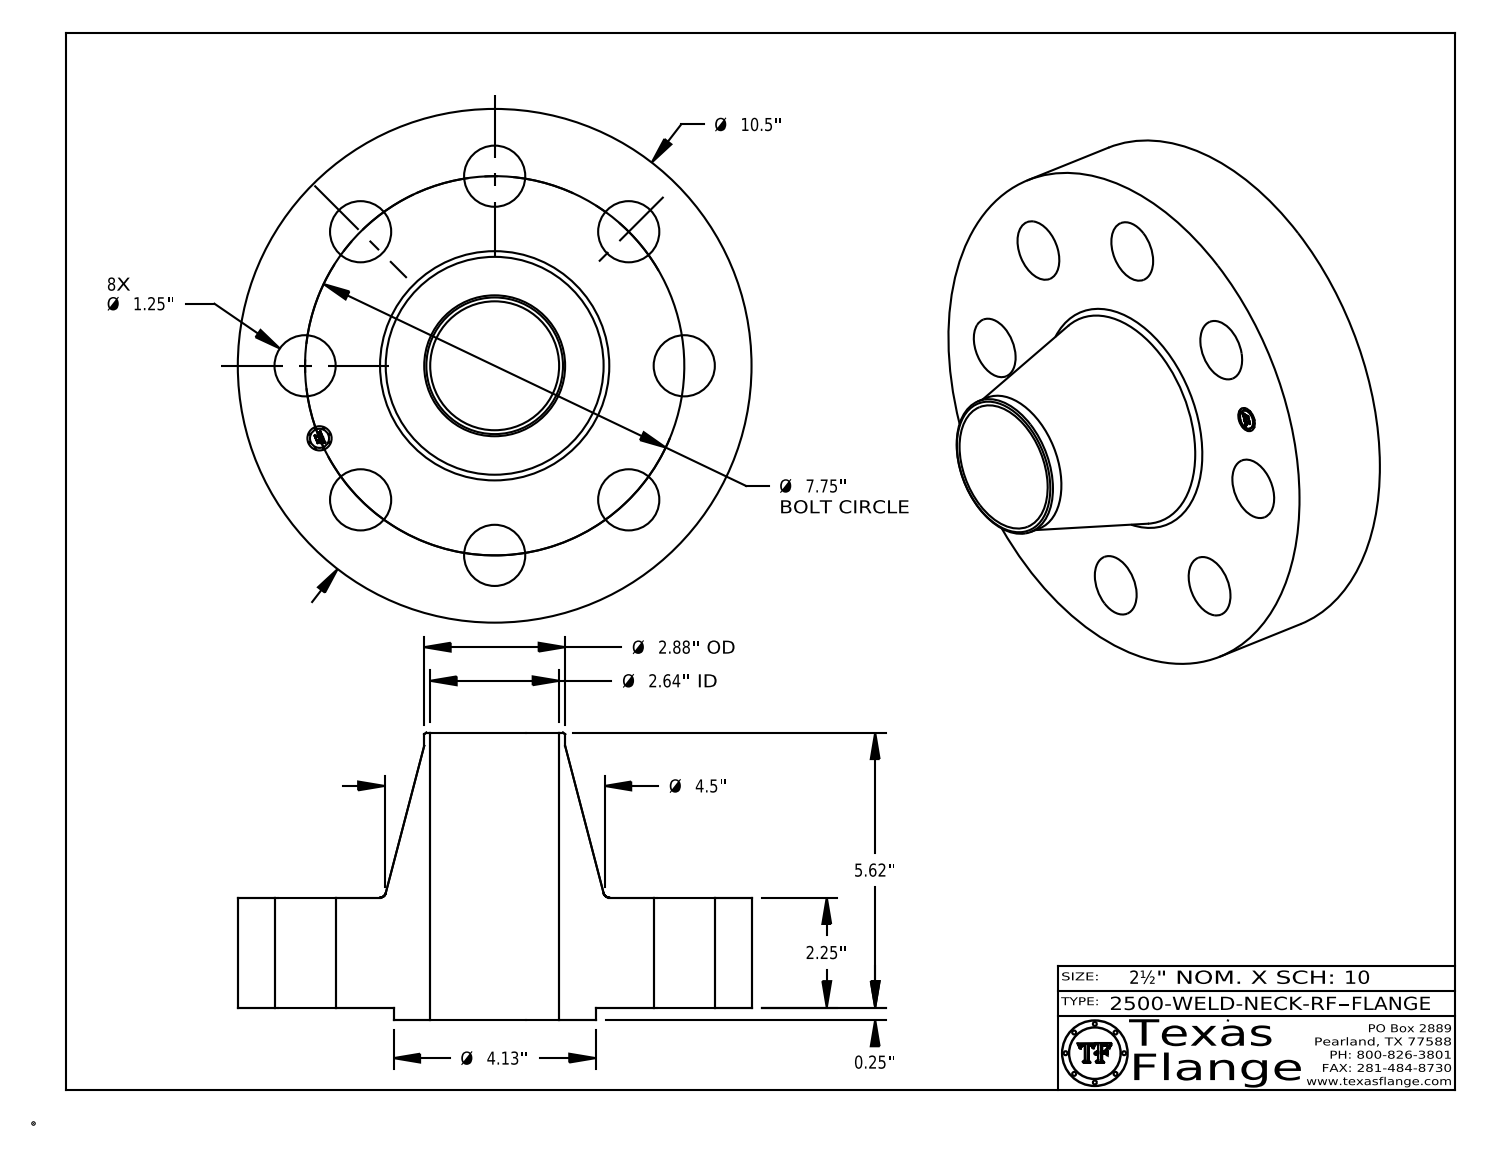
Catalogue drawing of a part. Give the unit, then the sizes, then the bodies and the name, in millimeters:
Units: millimetres
Overall size (bounding box): 266.7 × 266.7 × 149.1
Round holes (diameter × count): ⌀31.8 ×8, ⌀12.6 ×1, ⌀66.9 ×1
Round bosses / shafts (diameter × count): ⌀0.8 ×8, ⌀266.7 ×1, ⌀104.9 ×1, ⌀73.2 ×1, ⌀9.9 ×1
Main face-to-face distances: 57.2, 6.4, 63.5, 149.1, 142.7, 85.6, 63.1, 56.8, 0.4, 86
Hole centre spacings: 75.3, 98.4, 139.2, 181.9, 196.9, 193.1, 38.4, 38.4
Volume: 2 941 000 mm³ · Surface area: 238 100 mm²
Bodies: 1 solid, 419 faces (369 planar, 44 cylindrical, 6 other)
Part name (STEP PRODUCT): 2500-WELD-NECK-RF
STEP written by: CATIA V5 STEP AP214 (AUTOMOTIVE_DESIGN)
